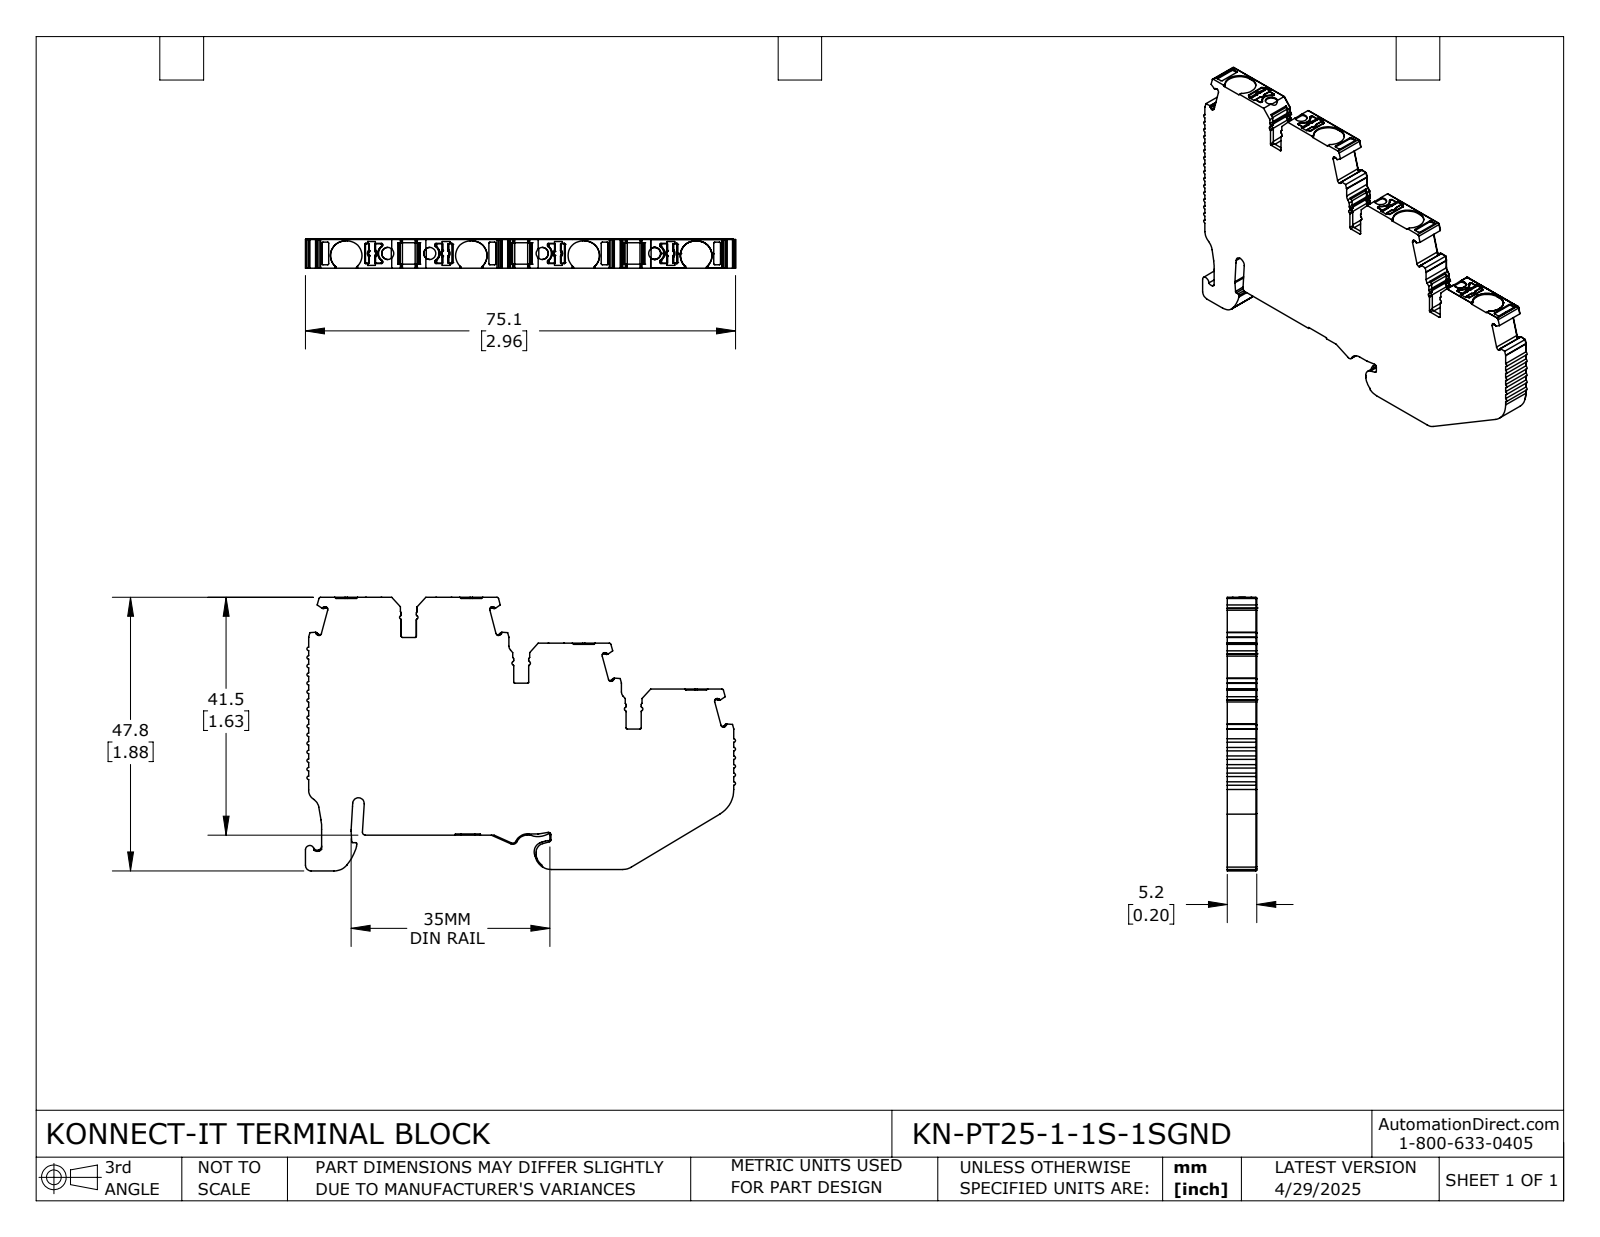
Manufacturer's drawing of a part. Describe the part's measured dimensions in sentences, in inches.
The part is named "KN-PT25-1-1S-1SGND". Its 3-D file was written by "SolidWorks 2024 (CONFIG_CONTROL_DESIGN)". It is 1 solid with 1004 faces: 482 planar, 451 cylindrical and 71 other. Overall it measures 2.957 by 1.88 by 0.203 inches. Its volume is 0.814 cubic inches and its surface area 10.77 square inches. Round holes: 4 of diameter 0.083. Partial cylindrical surfaces (rounded edges, fillets, slot ends): 92 of radius 0.008, 60 of radius 0.012, 35 of radius 0.004, 16 of radius 0.006, 16 of radius 0.02, 15 of radius 0.016, 8 of radius 0.006, 8 of radius 0.01. The main face-to-face distances are 0.203, 0.315, 0.63, 0.236, 0.315, 0.323, 0.079, 0.773, 1.626, 1.311. The hole center spacings are 0.289, 0.773, 0.773, 1.062, 1.546, 1.835.
